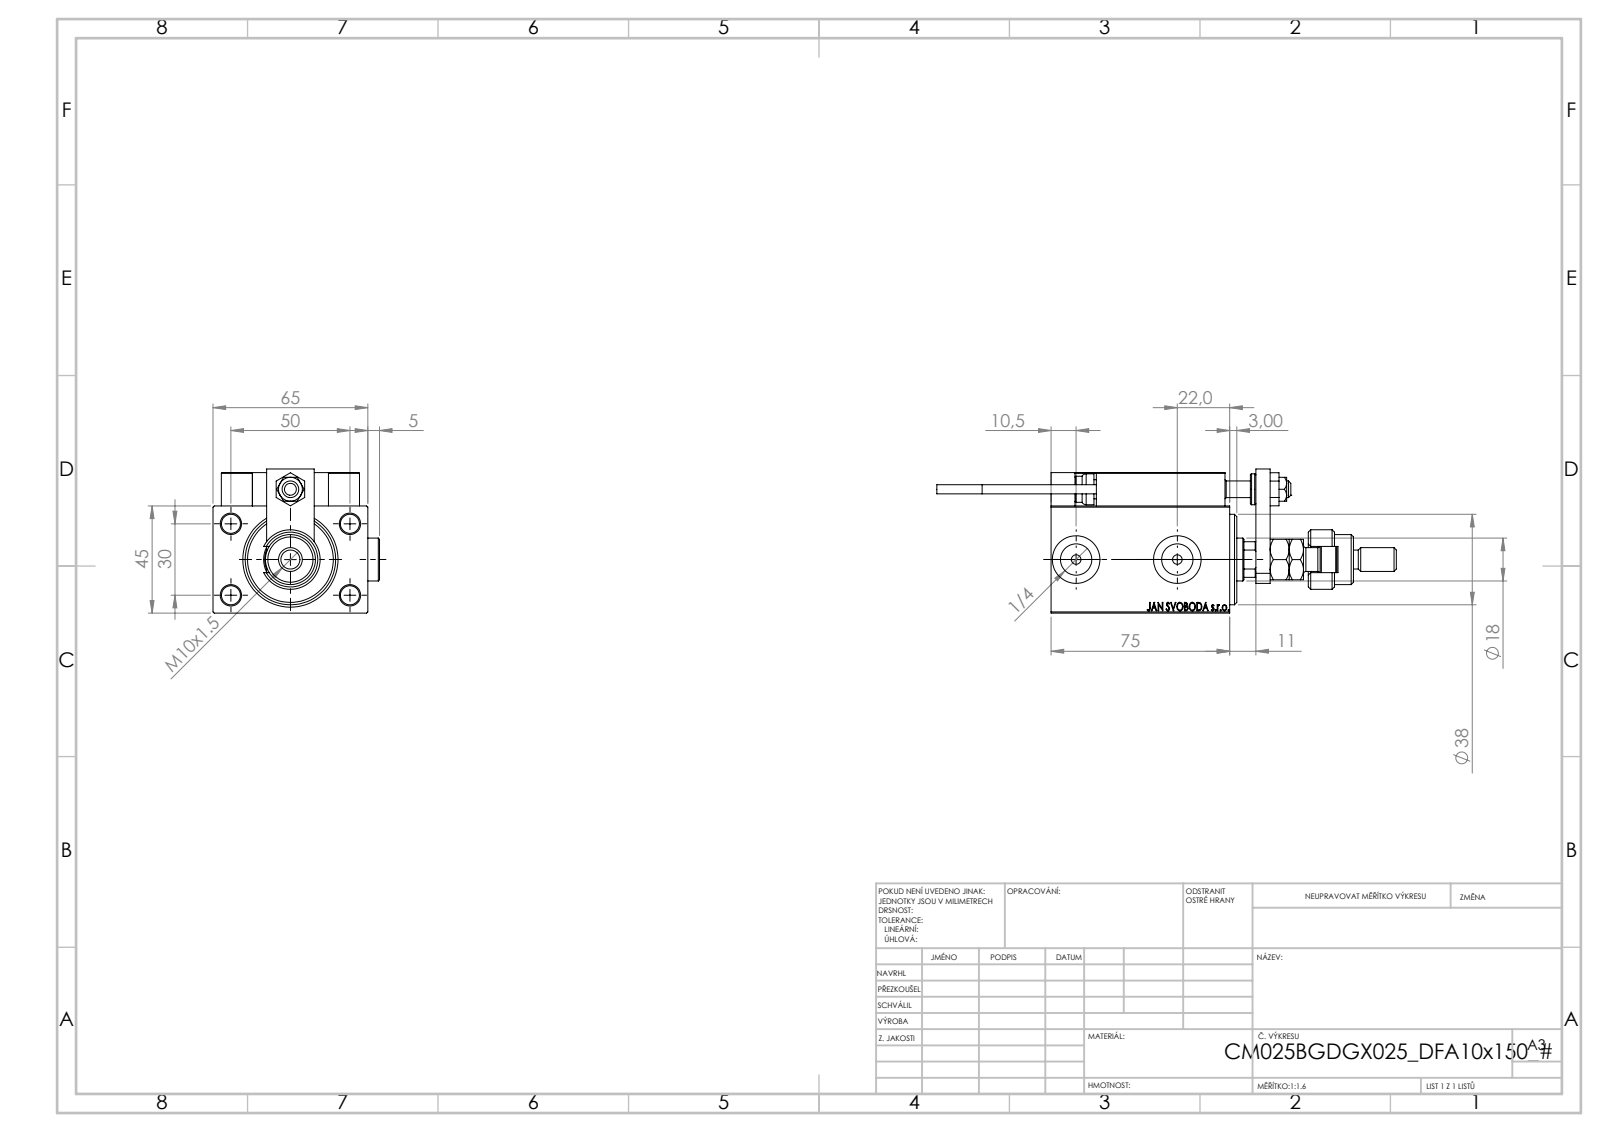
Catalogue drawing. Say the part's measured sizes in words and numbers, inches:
The part is named "KONCOVKA; FEMALE_PART_FOR_DFA; Zatka_OIL_PORT; V450CM_VC_B (+7 more)". Its 3-D file was written by "SolidWorks 2019 (CONFIG_CONTROL_DESIGN)". It is 28 solids with 1457 faces: 623 planar, 213 cylindrical and 621 other. Overall it measures 7.598 by 2.752 by 2.382 inches. Its volume is 16.05 cubic inches and its surface area 115.6 square inches. Round holes: 9 of diameter 0.315, 6 of diameter 0.157, 4 of diameter 0.126, 2 of diameter 0.197, 2 of diameter 0.518, 2 of diameter 0.787, 1 of diameter 0.276, 1 of diameter 0.335, 1 of diameter 0.571, 1 of diameter 0.709, 1 of diameter 0.846, 1 of diameter 0.886. Round bosses or shafts: 2 of diameter 0.709, 2 of diameter 0.197, 2 of diameter 0.15, 1 of diameter 0.984, 1 of diameter 0.827, 1 of diameter 0.63, 1 of diameter 0.512, 1 of diameter 0.433. Partial cylindrical surfaces (rounded edges, fillets, slot ends): 30 of radius 0.012, 2 of radius 0.118, 1 of radius 0.217, 1 of radius 0.335, 1 of radius 0.344. The main face-to-face distances are 1.772, 0.551, 2.559, 0.236, 2.323, 0.748, 0.197, 0.512, 3.386, 0.138. The hole center spacings are 1.148, 0.448, 0.787, 1.066, 1.138, 1.165, 1.169, 1.181.
